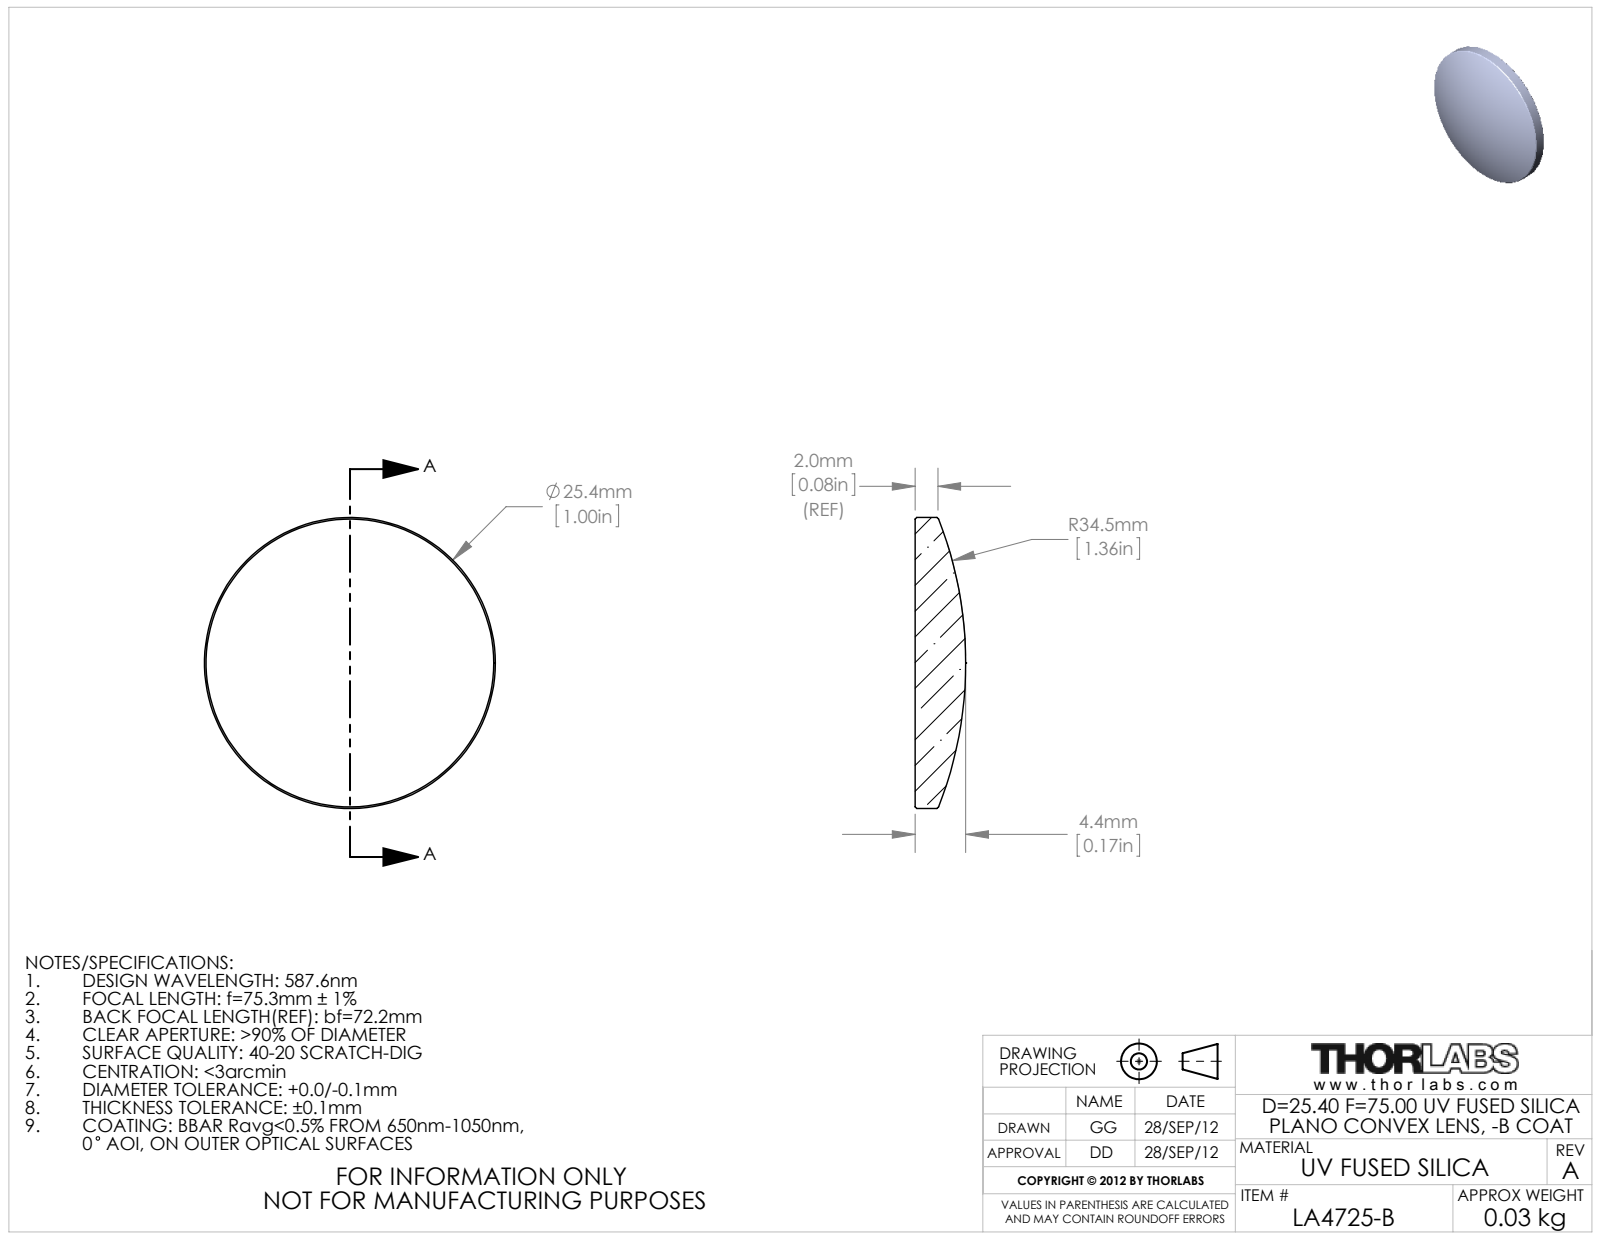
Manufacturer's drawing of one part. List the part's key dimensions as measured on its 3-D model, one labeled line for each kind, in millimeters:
Part name (STEP PRODUCT): 24985-E0W
STEP written by: SolidWorks 2011 (CONFIG_CONTROL_DESIGN)
Units: millimetres
Bodies: 1 solid, 9 faces (1 planar, 2 cylindrical, 6 other)
Overall size (bounding box): 25.4 × 25.4 × 4.42
Volume: 1 633 mm³ · Surface area: 1 182 mm²
Round bosses / shafts (diameter × count): ⌀25.4 ×1
